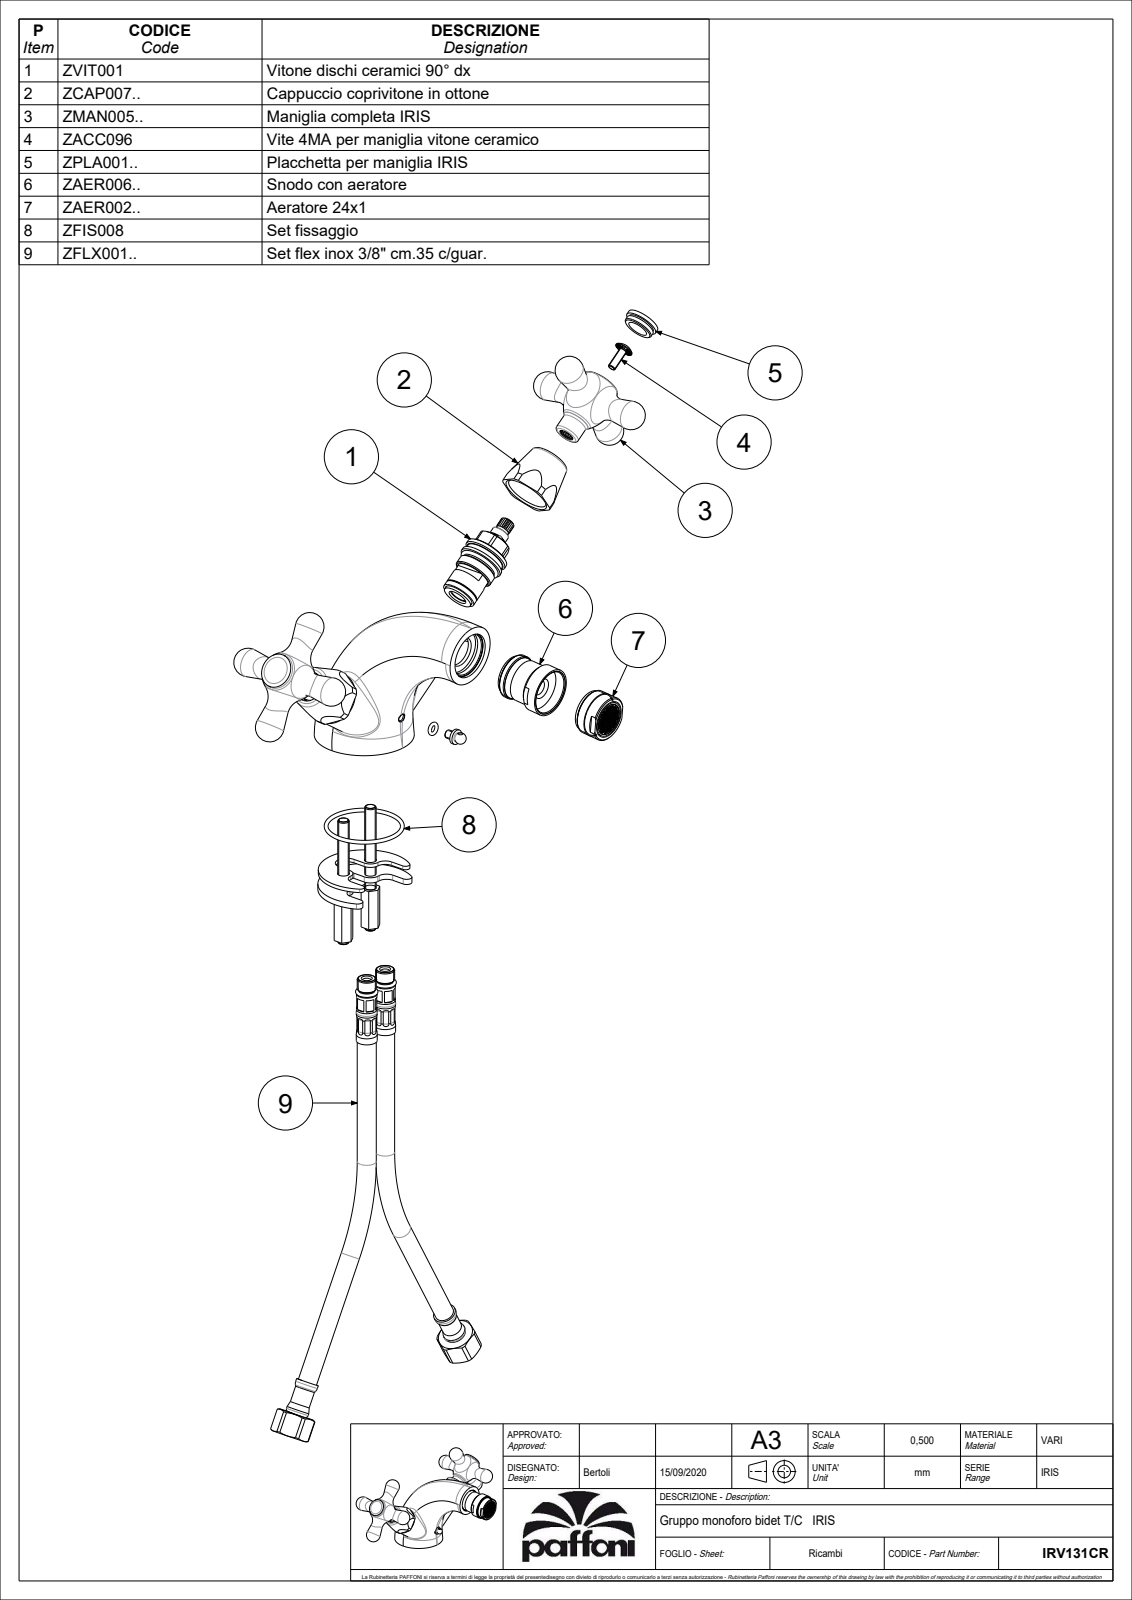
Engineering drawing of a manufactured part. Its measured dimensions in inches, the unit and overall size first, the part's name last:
Units: inches
Overall size (bounding box): 7.42 × 5.122 × 3.61
Round holes (diameter × count): ⌀0.217 ×2, ⌀0.305 ×2, ⌀0.315 ×2, ⌀0.354 ×2, ⌀0.433 ×2, ⌀0.732 ×2, ⌀0.846 ×2, ⌀1.673 ×1
Round bosses / shafts (diameter × count): ⌀1.083 ×2, ⌀0.709 ×2, ⌀0.531 ×2, ⌀1.476 ×1, ⌀1.016 ×1, ⌀0.945 ×1, ⌀0.886 ×1, ⌀0.394 ×1
Partial cylindrical surfaces — rounded edges, fillets, slot ends (radius × count): R0.571 ×2
Main face-to-face distances: 1.043, 0.862, 1.13, 0.118, 1.012, 1.811, 0.949, 0.079, 0.945, 0.866
Hole centre spacings: 0.432, 0.476, 0.53, 0.89, 0.591, 0.866
Volume: 14.7 in³ · Surface area: 69.09 in²
Bodies: 1 solid, 285 faces (66 planar, 64 cylindrical, 155 other)
Part name (STEP PRODUCT): IRV131CR
STEP written by: CREO PARAMETRIC BY PTC INC, 2020044 (CONFIG_CONTROL_DESIGN)
